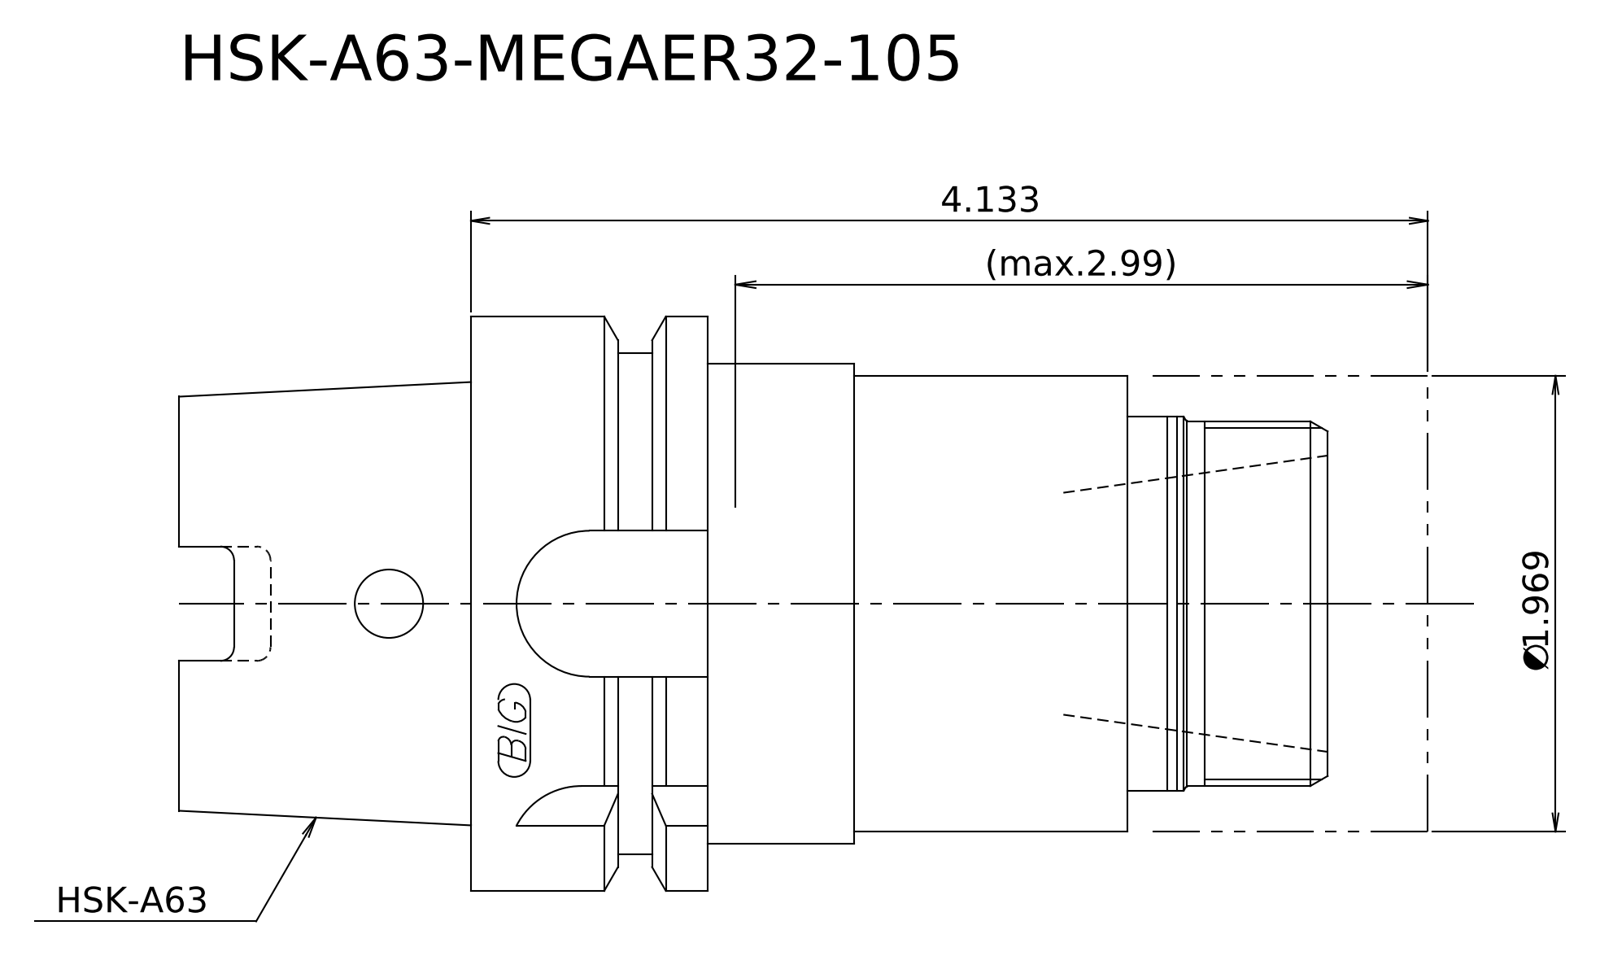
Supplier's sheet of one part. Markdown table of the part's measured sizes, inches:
| quantity | value |
| --- | --- |
| STEP written by | Kubotek KeyCreator 2011 V10.0.2 (22737) (automotive_design) |
| units | inches |
| bodies | 2 solids, 23 faces (10 planar, 8 cylindrical, 5 other) |
| overall size | 5.394 × 2.48 × 2.48 |
| volume | 19.16 in³ |
| surface area | 55.02 in² |
| round bosses / shafts (diameter × count) | 2.48 × 1, 2.165 × 1, 2.071 × 1, 1.969 × 1, 1.614 × 1, 1.575 × 1 |
| main face-to-face distances | 1.189, 5.394, 4.205, 4.134, 2.945, 1.26, 0.433, 0.756, 3.701, 4.961 |
